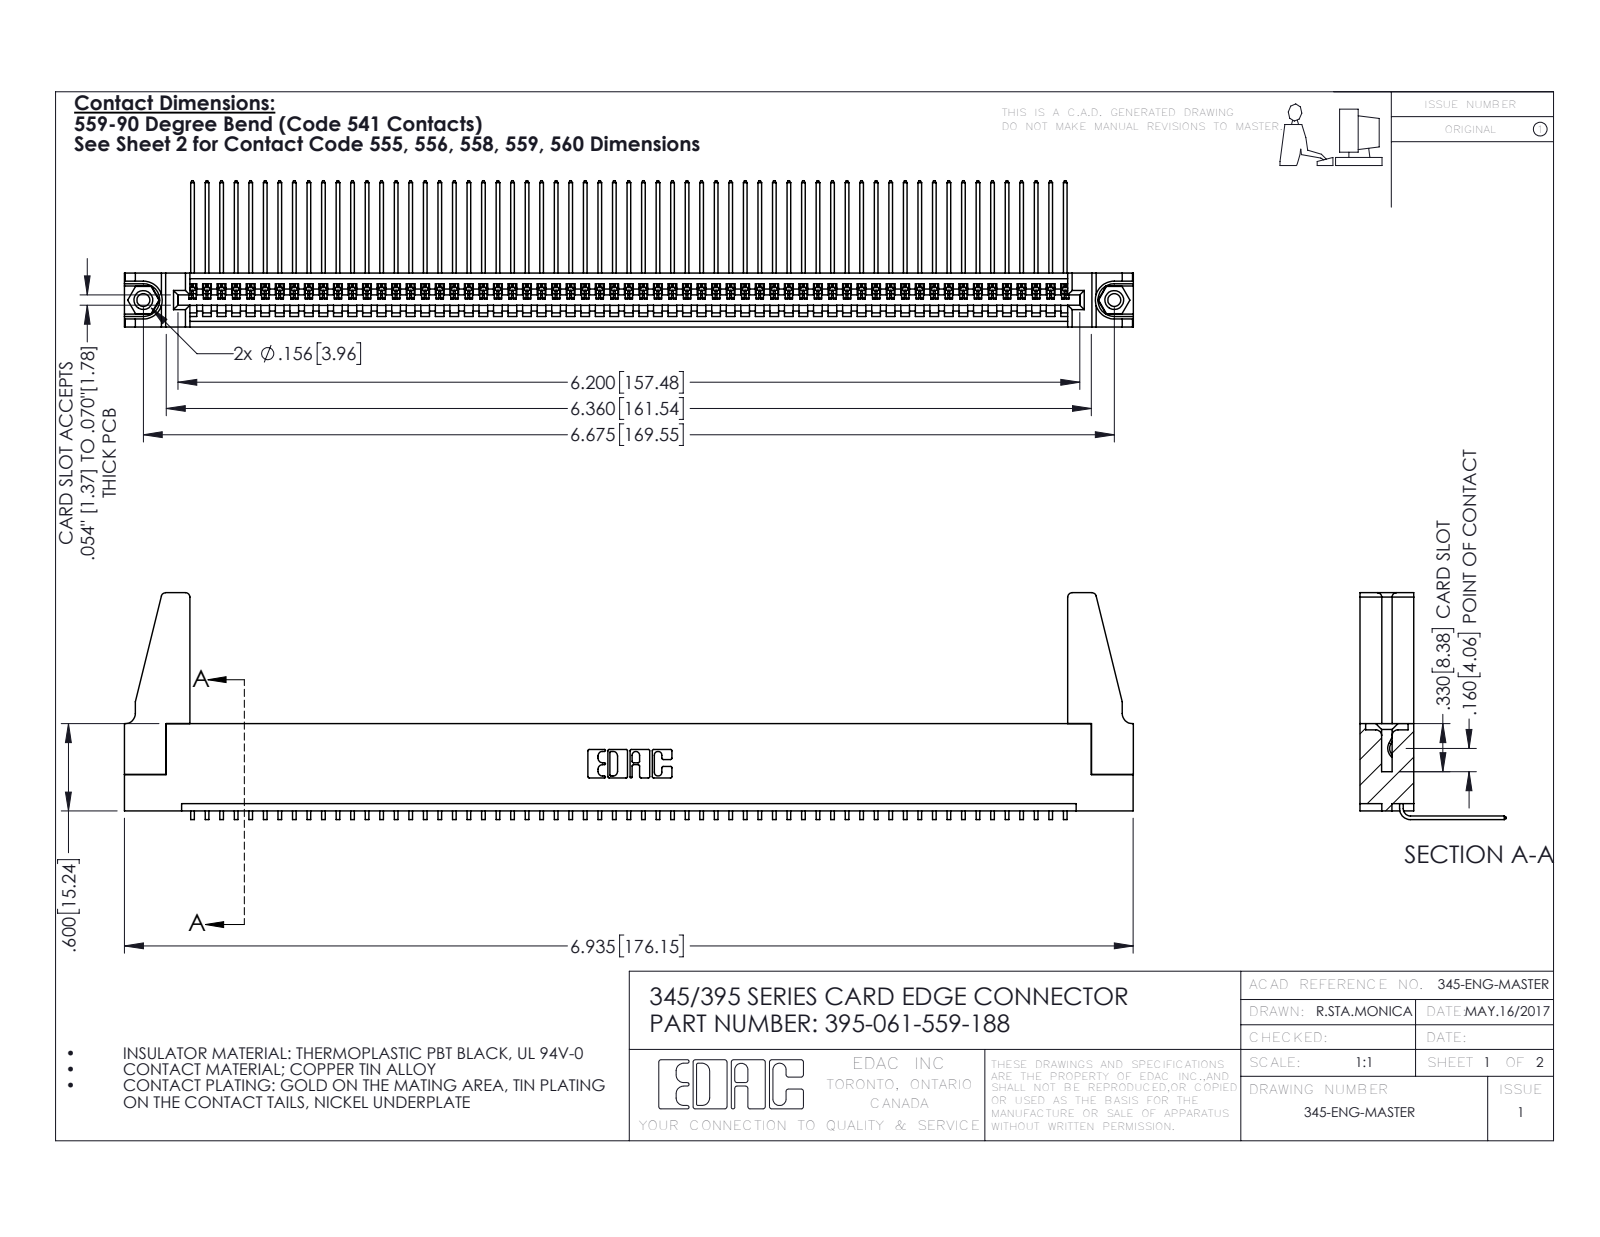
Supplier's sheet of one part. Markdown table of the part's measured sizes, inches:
| quantity | value |
| --- | --- |
| part name | 345-220-078_345-220-088; 395-061-559-188; 345 Part_Flush Mounting Lugs - 0.156 Dia-TH; 345-250-001_345-250-001-102 (+1 more) |
| STEP written by | SolidWorks 2016 (CONFIG_CONTROL_DESIGN) |
| units | inches |
| bodies | 66 solids, 3910 faces (2714 planar, 1180 cylindrical, 16 other) |
| overall size | 6.936 × 1.559 × 1.005 |
| volume | 1.242 in³ |
| surface area | 42.31 in² |
| round holes (diameter × count) | 0.089 × 2, 0.125 × 2, 0.156 × 2, 0.064 × 1 |
| round bosses / shafts (diameter × count) | 0.155 × 2 |
| partial cylindrical surfaces (radius × count) | 0.006 × 122, 0.01 × 22, 0.03 × 8, 0.007 × 6, 0.031 × 6, 0.026 × 3, 0.031 × 2, 0.04 × 2 |
| main face-to-face distances | 0.072, 0.298, 0.37, 0.2, 0.098, 0.272, 0.025, 0.225, 0.149, 0.072 |
| hole center spacings | 0.27, 6.439, 6.675 |
